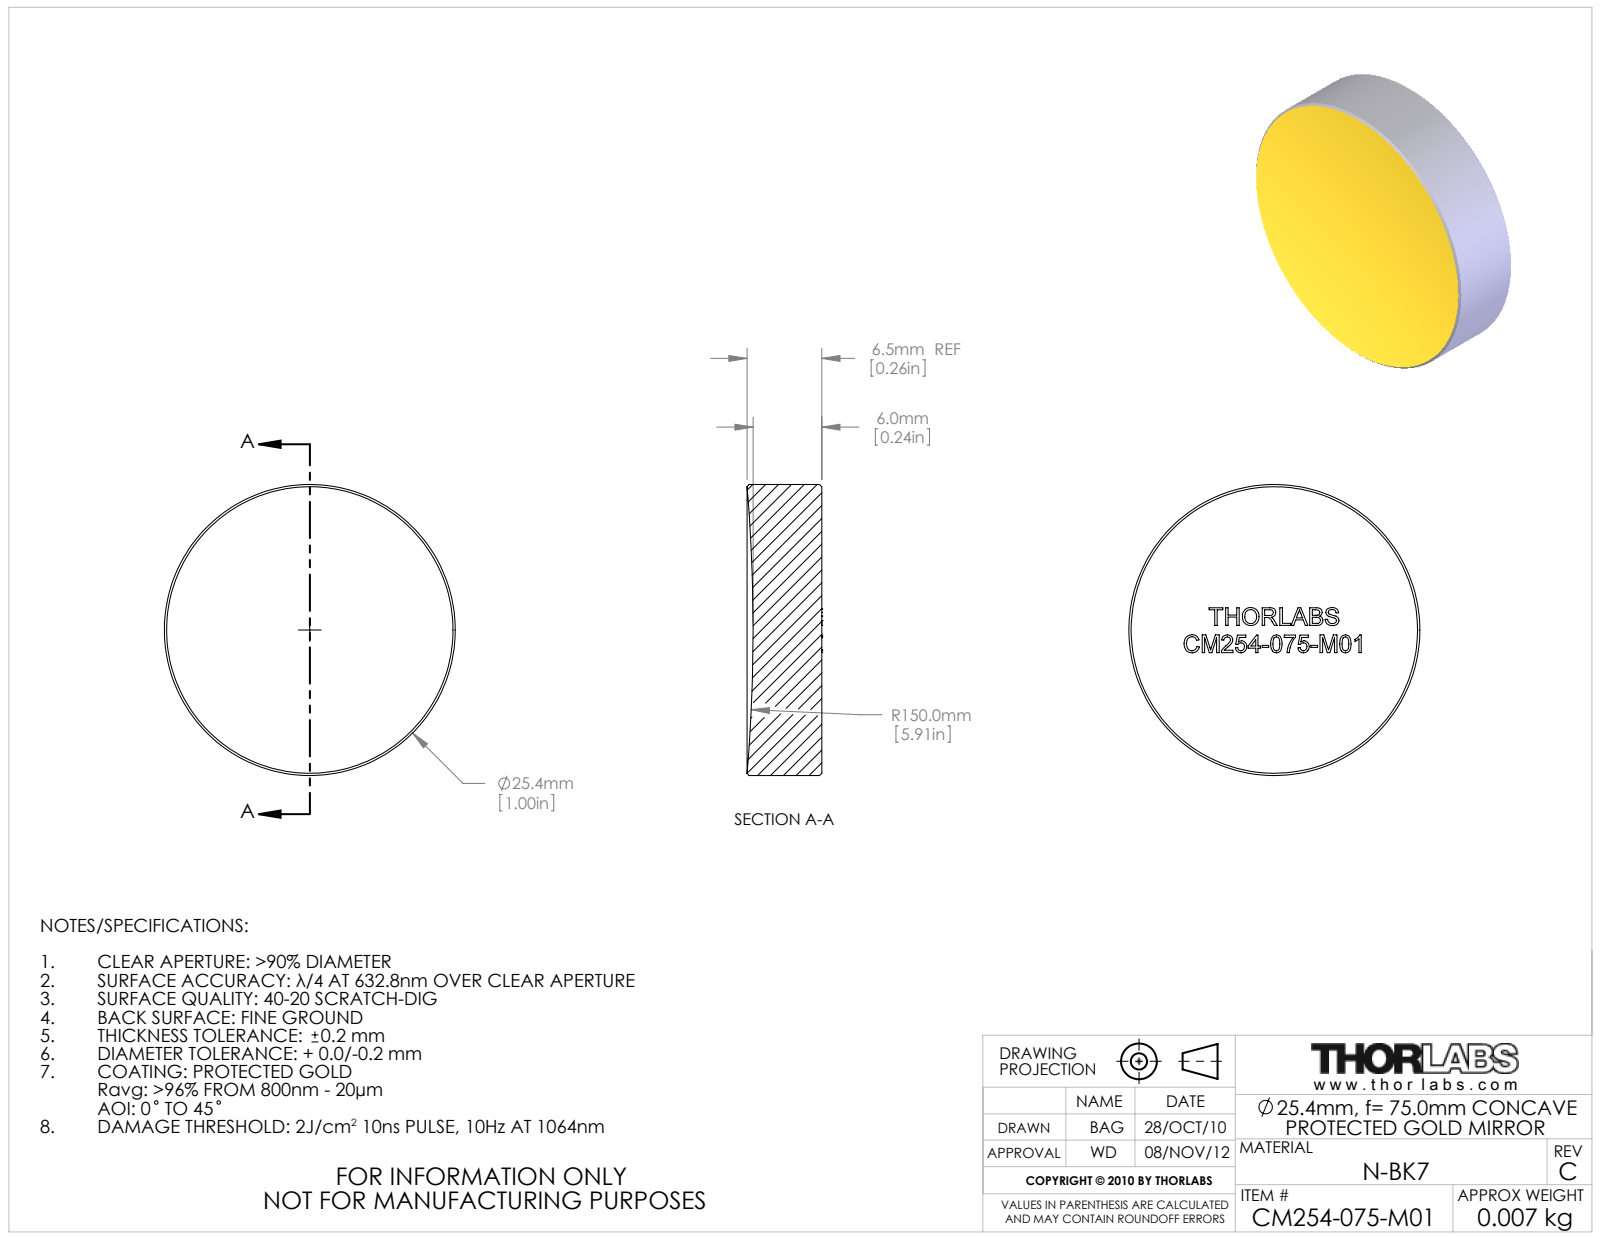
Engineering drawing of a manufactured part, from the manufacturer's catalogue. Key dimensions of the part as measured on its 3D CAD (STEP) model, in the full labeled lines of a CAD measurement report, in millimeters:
Part name (STEP PRODUCT): 17584-E0W
STEP written by: SolidWorks 2009 (AUTOMOTIVE_DESIGN)
Units: millimetres
Bodies: 1 solid, 281 faces (167 planar, 2 cylindrical, 112 other)
Overall size (bounding box): 25.4 × 25.4 × 6.5
Volume: 3 180 mm³ · Surface area: 1 516 mm²
Round bosses / shafts (diameter × count): ⌀25.4 ×1
Main face-to-face distances: 1.5, 1.9, 2.4, 10.3, 2.4, 0.9, 1.3, 1.1, 1.5, 1
